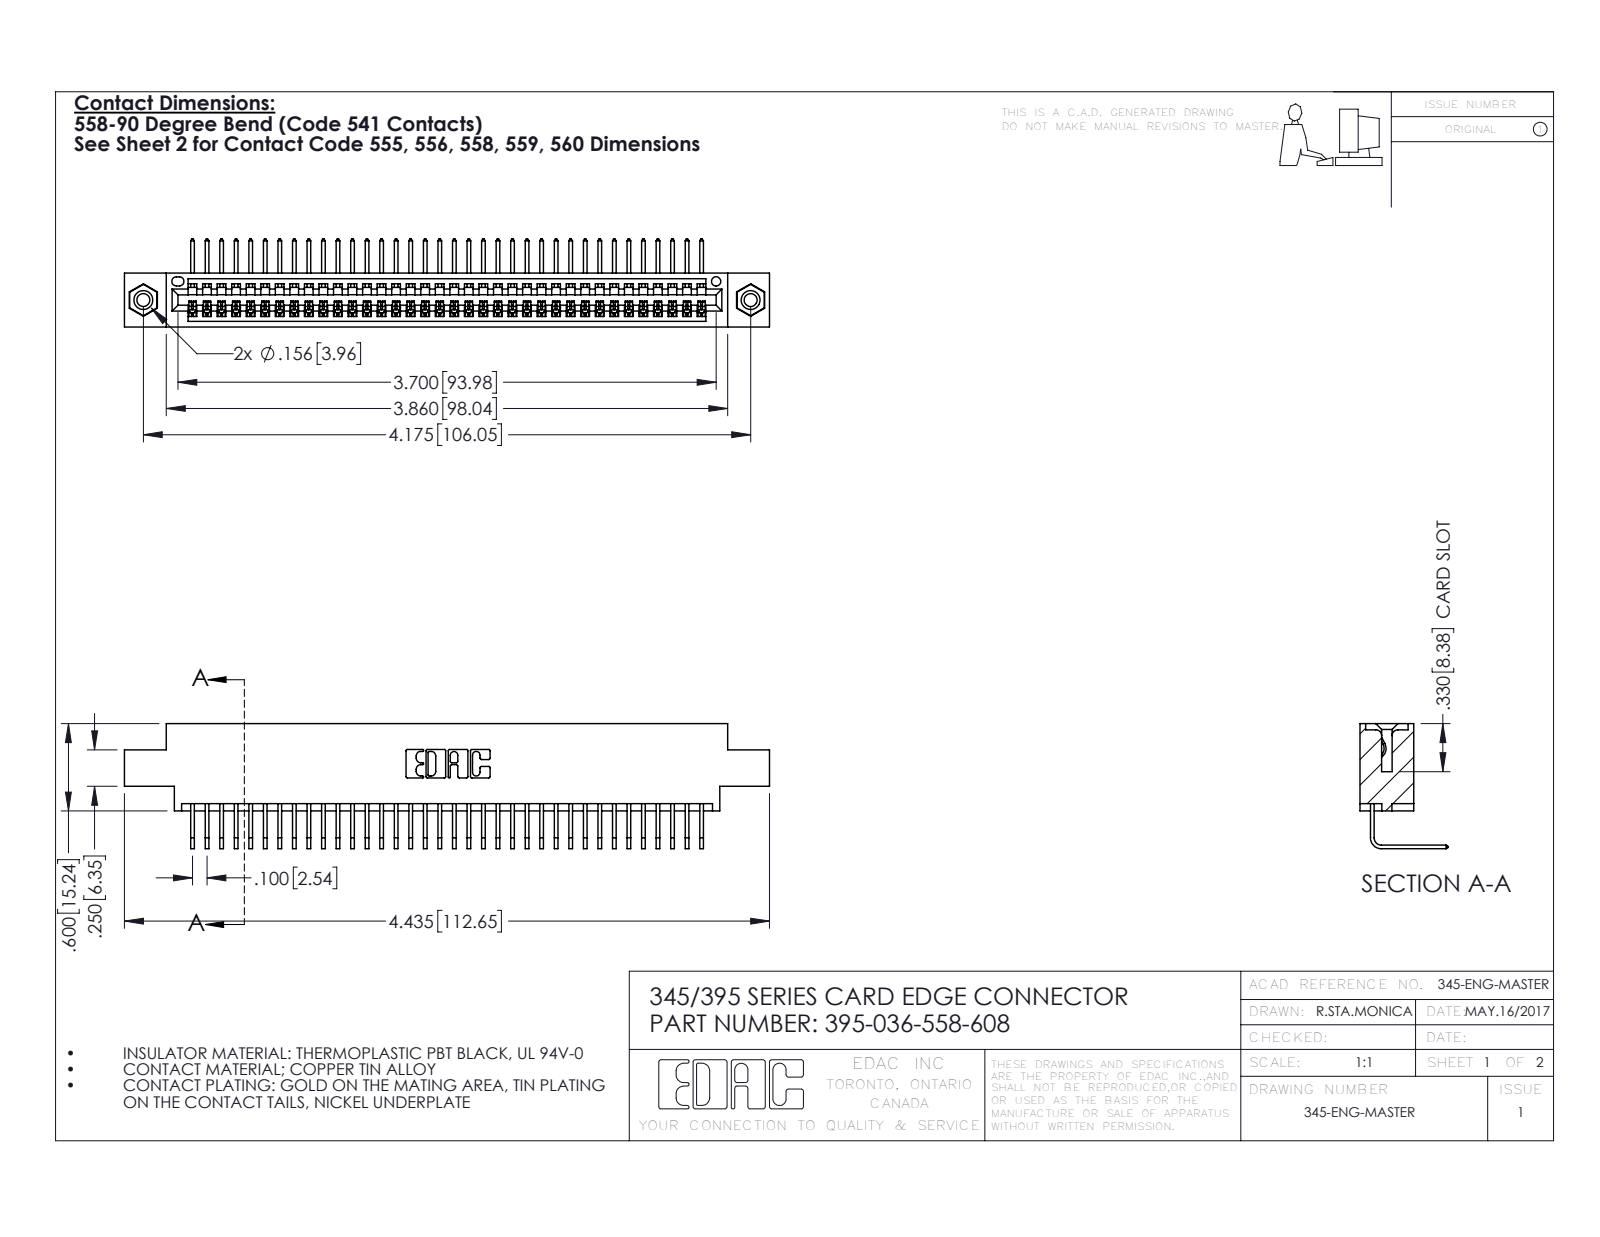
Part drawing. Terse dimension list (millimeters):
name: 345-292-001_558 Tail - 2; 395-036-558-608; 345 Part_0.170 Offset - 0.156 Dia-TI; 345-250-001_345-250-003-102
written by: SolidWorks 2016 (CONFIG_CONTROL_DESIGN)
unit: mm
bodies: 39 solids, 2350 faces (1628 planar, 706 cylindrical, 16 other)
size: 112.6 × 21.8 × 15.4
volume: 10 700 mm³; area: 14 920 mm²
holes: 2× ⌀2.3, 2× ⌀3.2, 2× ⌀4, 1× ⌀1.6
bosses: 2× ⌀3.9
rounds: 72× R0.2, 22× R0.3, 6× R0.2, 6× R0.8, 3× R0.7, 2× R0.8, 2× R1, 1× R0.4
face distances: 1.8, 7.6, 9.4, 5.1, 2.5, 6.9, 0.6, 5.7, 4.4, 3.8
hole spacings: 6.9, 100.1, 106
